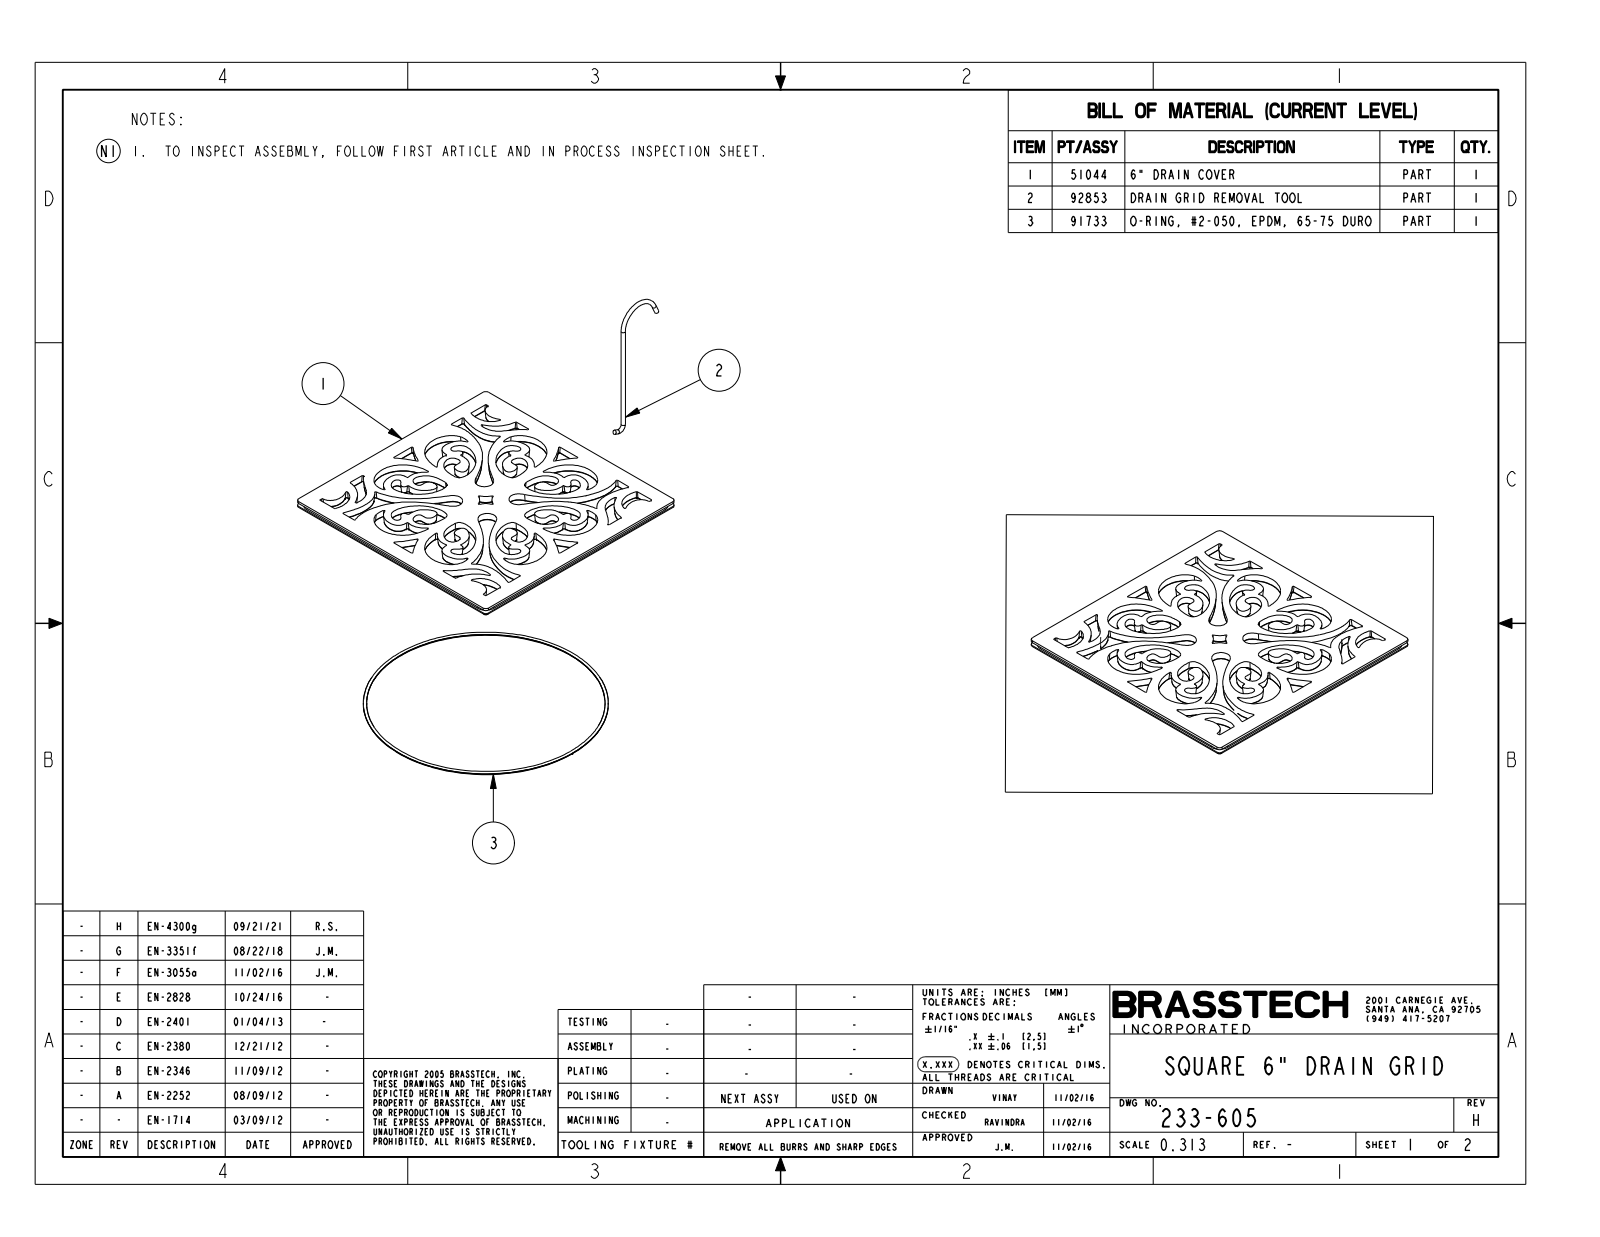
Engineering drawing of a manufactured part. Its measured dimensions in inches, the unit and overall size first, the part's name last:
Units: inches
Overall size (bounding box): 5.895 × 5.895 × 0.188
Partial cylindrical surfaces — rounded edges, fillets, slot ends (radius × count): R0.02 ×4, R0.08 ×4, R0.25 ×4
Main face-to-face distances: 0.188, 0.041, 5.854, 0.134, 0.054, 0.054, 0.08, 0.134, 5.895, 5.812
Volume: 3.993 in³ · Surface area: 71.68 in²
Bodies: 1 solid, 429 faces (40 planar, 32 cylindrical, 357 other)
Part name (STEP PRODUCT): 51044
STEP written by: CREO PARAMETRIC BY PTC INC, 2018400 (AUTOMOTIVE_DESIGN)
